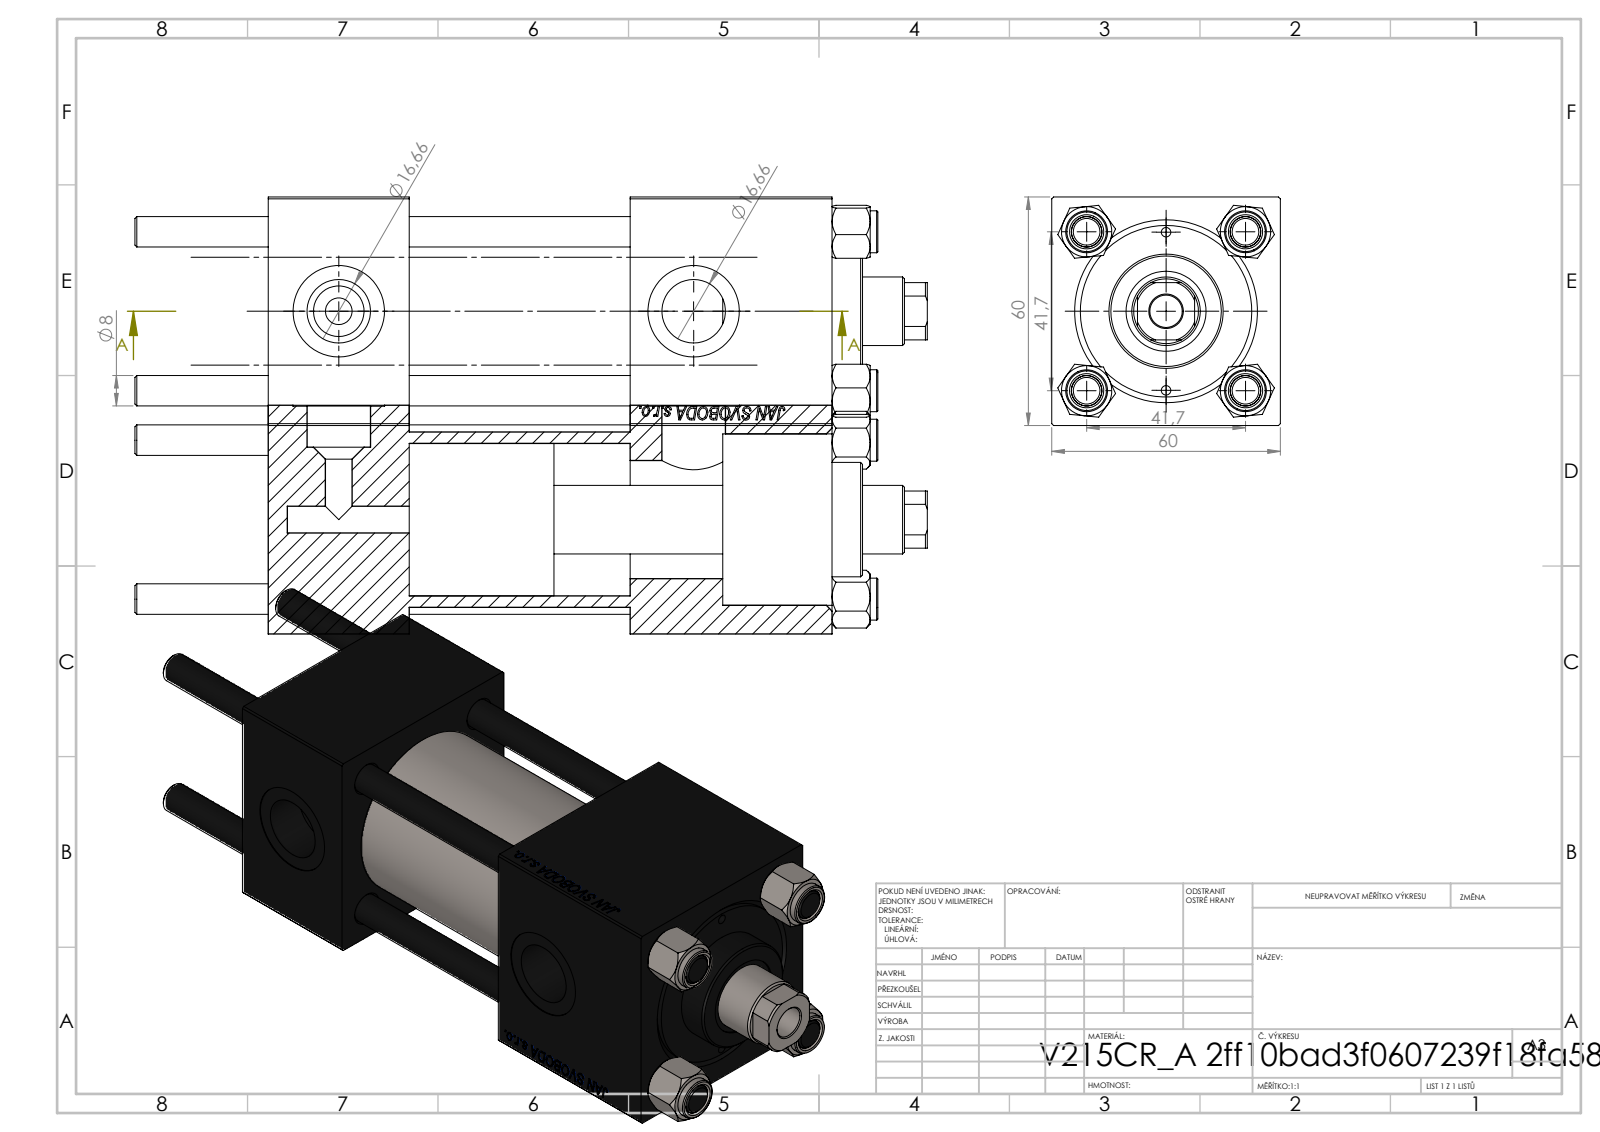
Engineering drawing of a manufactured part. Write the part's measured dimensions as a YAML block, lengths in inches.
part_name: "CR025_012_A_0_G_A_G_M_020_+#_##_TYCINKA; V215CR_VCP; V215CR_BODY_A; NUT_M5 (+1 more)"
step_written_by: "SolidWorks 2019 (CONFIG_CONTROL_DESIGN)"
units: inches
bodies: {solids: 11, faces: 1139, planar: 520, cylindrical: 83, other: 536}
overall_size: [8.189, 2.362, 2.362]
volume: 25.23
surface_area: 176.8
round_holes:
  - {diameter: 0.315, count: 4}
  - {diameter: 0.098, count: 2}
  - {diameter: 0.276, count: 2}
  - {diameter: 0.656, count: 2}
  - {diameter: 0.945, count: 2}
  - {diameter: 0.335, count: 1}
  - {diameter: 0.709, count: 1}
  - {diameter: 0.827, count: 1}
  - {diameter: 1.22, count: 1}
  - {diameter: 1.575, count: 1}
  - {diameter: 1.772, count: 1}
round_bosses_or_shafts:
  - {diameter: 0.433, count: 4}
  - {diameter: 1.811, count: 1}
  - {diameter: 1.181, count: 1}
partial_cylinders:
  - {radius: 0.335, count: 1}
face_to_face_distances: [2.362, 1.457, 5.827, 4.37, 2.283, 2.087, 3.74, 4.697, 3.24, 0.957]
hole_center_spacings: [0.821, 1.161, 1.642, 1.832, 0.817, 2.322, 1.634, 3.668]
